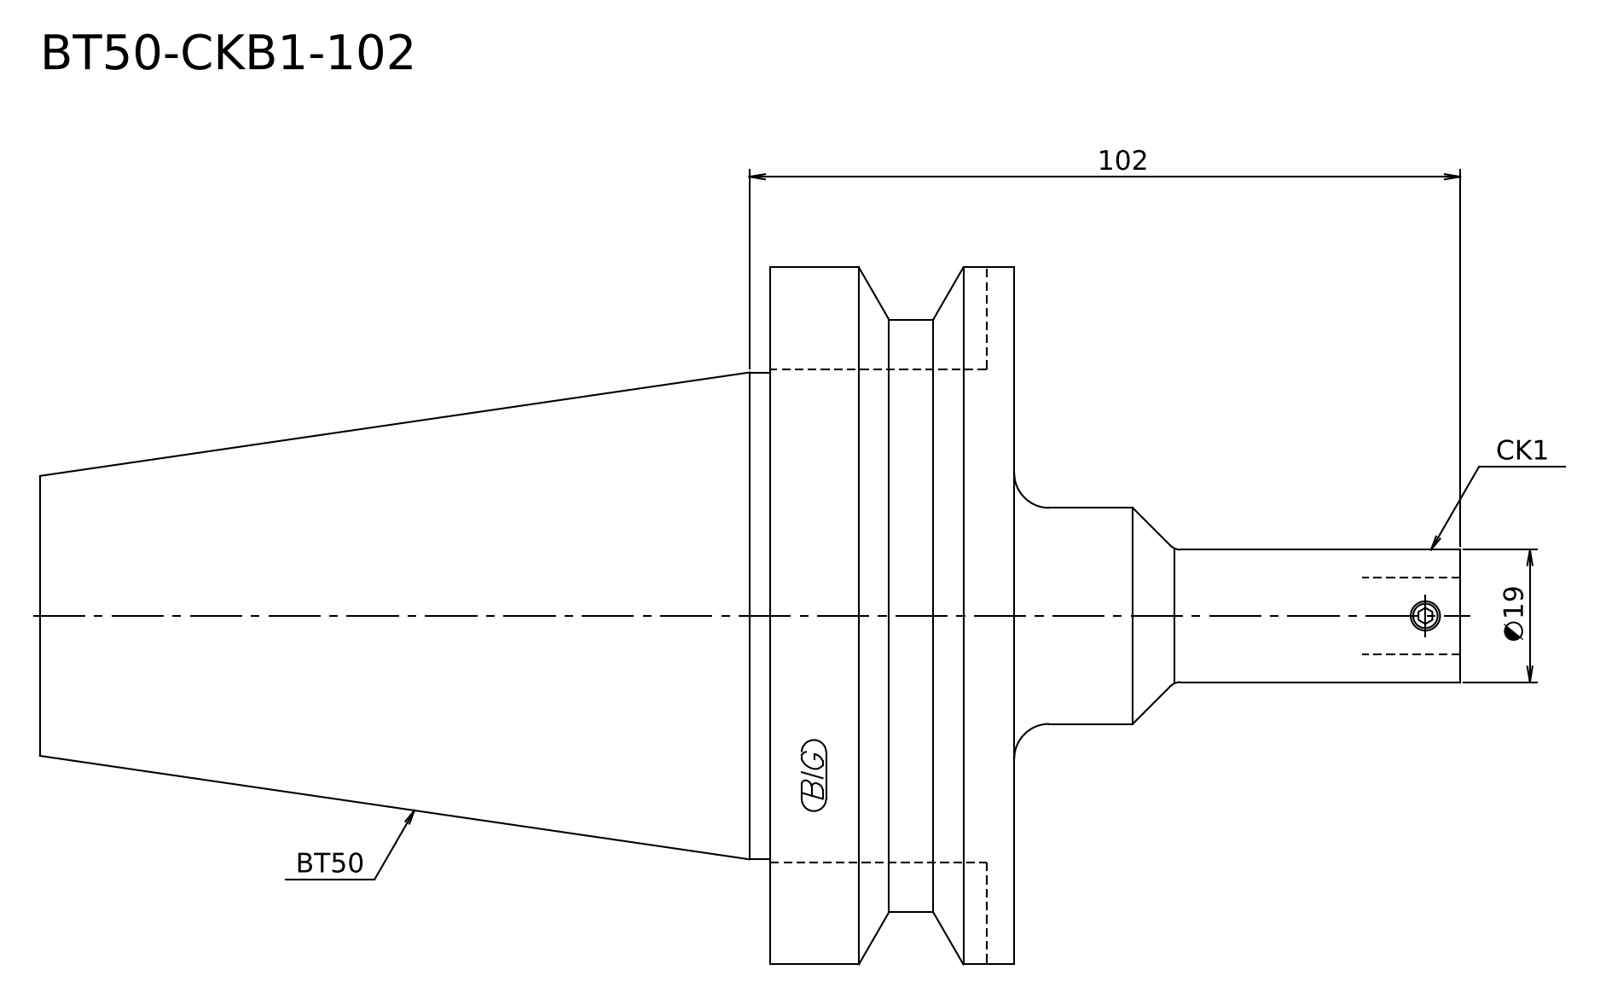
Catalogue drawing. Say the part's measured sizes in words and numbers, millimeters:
Its 3-D file was written by "Kubotek KeyCreator V8.5.1 (14335) (CONFIG_CONTROL_DESIGN)". It is 1 solid with 16 faces: 4 planar, 6 cylindrical and 6 other. Overall it measures 203.8 by 100 by 100 millimeters. Its volume is 539 372 cubic millimeters and its surface area 48 619 square millimeters. Round bosses or shafts: 1 of diameter 100, 1 of diameter 85, 1 of diameter 69.85, 1 of diameter 31, 1 of diameter 19. The main face-to-face distances are 35, 139.8, 104.8, 64, 99, 203.8.
